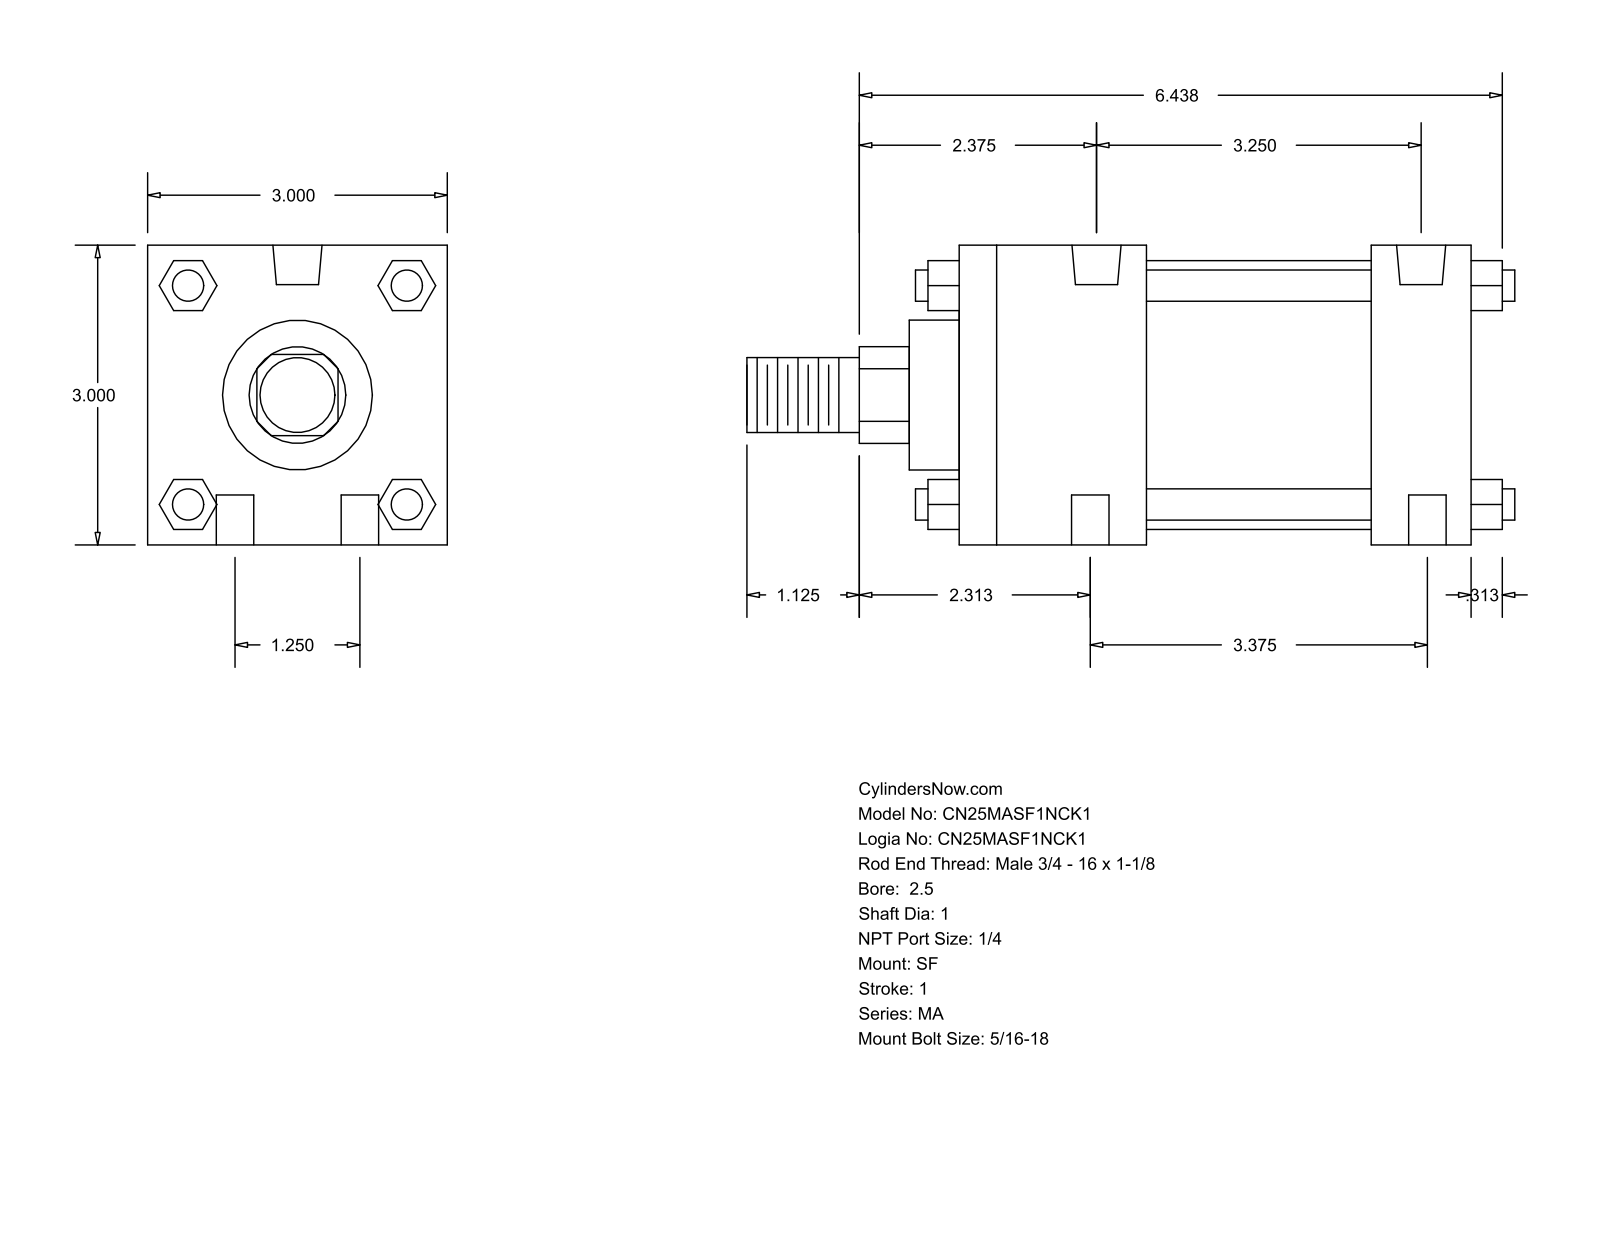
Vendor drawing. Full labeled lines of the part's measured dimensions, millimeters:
Part name (STEP PRODUCT): MA_SF__0250_1
STEP written by: GSSL Pune (CONFIG_CONTROL_DESIGN)
Units: millimetres
Bodies: 0 solids, 124 faces (94 planar, 30 cylindrical, 0 other)
Overall size (bounding box): 195.26 × 76.2 × 76.2
Round holes (diameter × count): ⌀9.53 ×4, ⌀7.94 ×2, ⌀12.49 ×2
Round bosses / shafts (diameter × count): ⌀7.94 ×4, ⌀68.33 ×1, ⌀38.1 ×1, ⌀25.4 ×1, ⌀19.05 ×1
Partial cylindrical surfaces — rounded edges, fillets, slot ends (radius × count): R12.29 ×1
Main face-to-face distances: 76.2, 130.17, 12.7, 104.78, 25.39, 47.63, 57.15, 82.54, 27.81, 48.17
Hole centre spacings: 15.96, 31.76, 82.55, 85.62, 85.63, 85.72, 91.41
